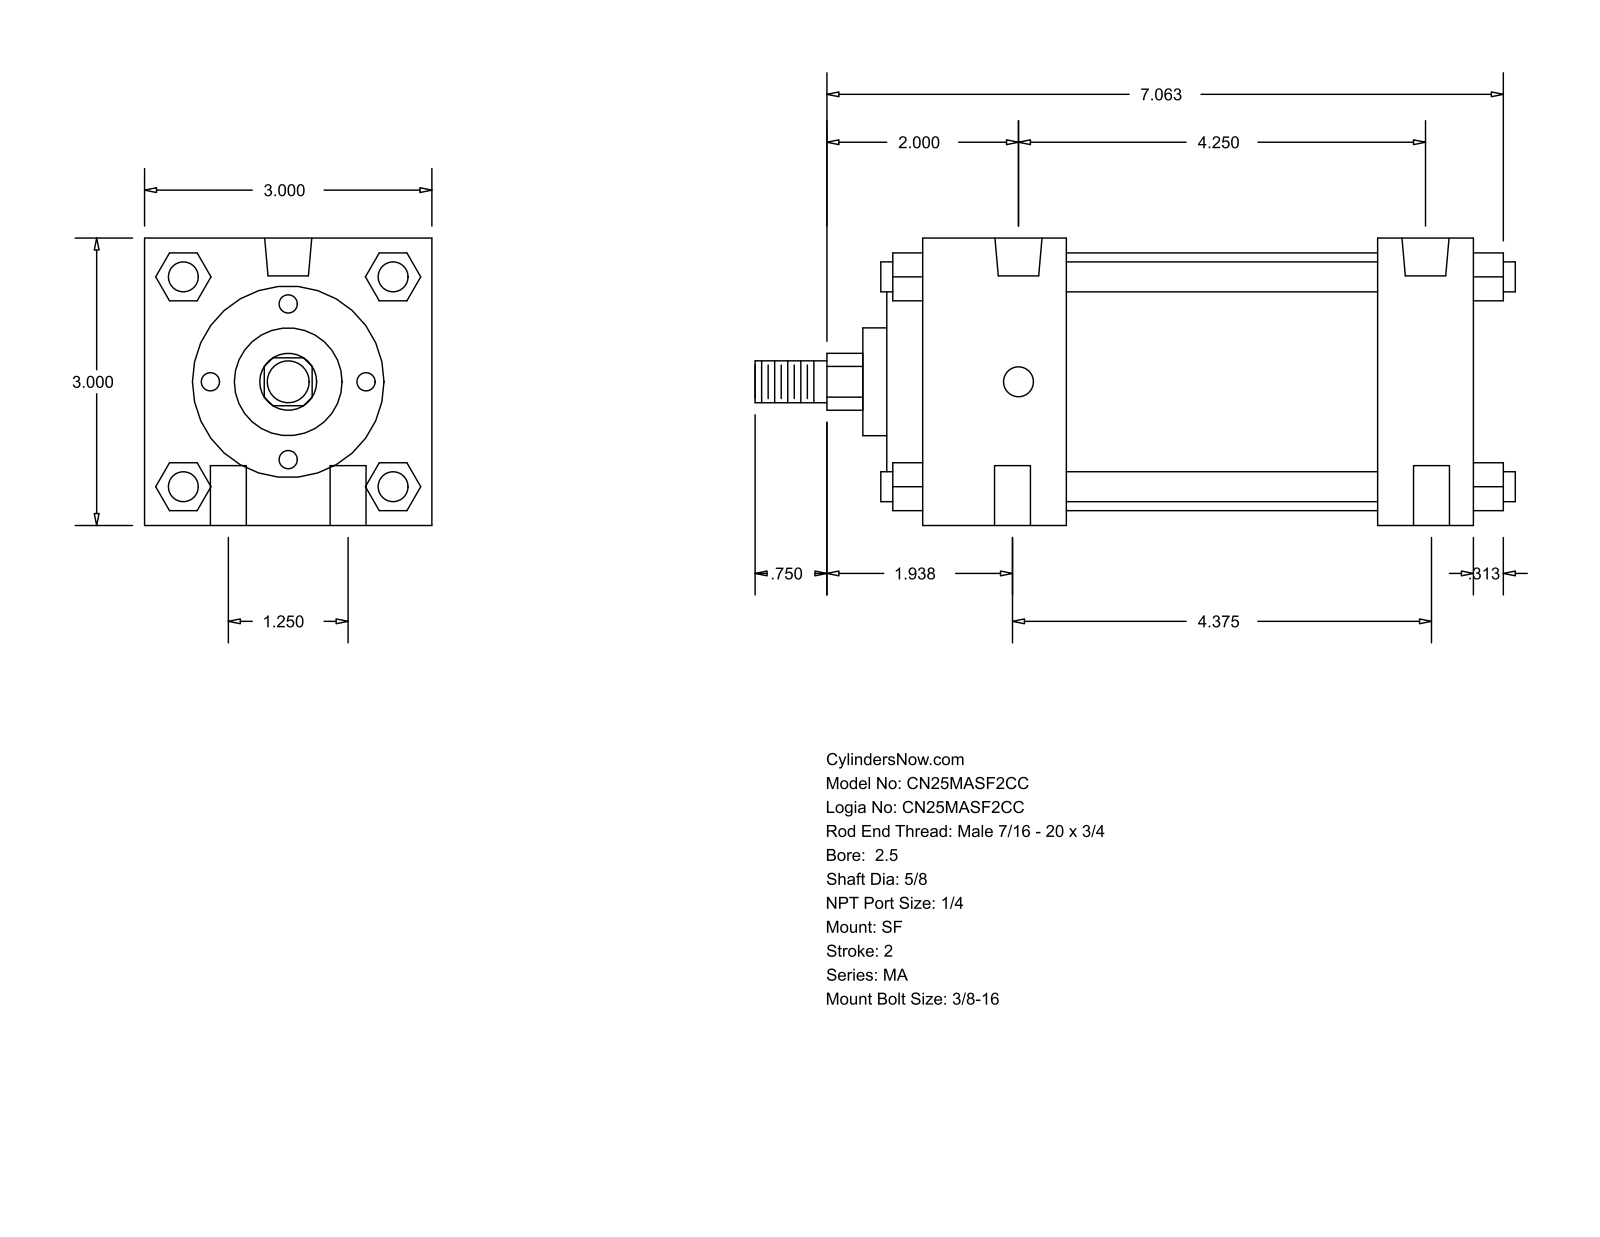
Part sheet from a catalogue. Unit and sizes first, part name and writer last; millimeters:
Units: millimetres
Overall size (bounding box): 201.61 × 76.2 × 76.2
Round holes (diameter × count): ⌀9.53 ×4, ⌀7.94 ×2, ⌀12.49 ×2
Round bosses / shafts (diameter × count): ⌀7.94 ×4, ⌀68.33 ×1, ⌀50.8 ×1, ⌀28.57 ×1, ⌀15.88 ×1, ⌀11.11 ×1
Partial cylindrical surfaces — rounded edges, fillets, slot ends (radius × count): R7.54 ×1
Main face-to-face distances: 76.2, 146.05, 25.4, 82.55, 120.65, 38.1, 107.95, 12.7, 9.52, 47.62
Hole centre spacings: 15.96, 110.69, 31.76, 107.95, 111.13, 115.58
Bodies: 0 solids, 126 faces (95 planar, 31 cylindrical, 0 other)
Part name (STEP PRODUCT): MA_SF__0250_0.625
STEP written by: GSSL Pune (CONFIG_CONTROL_DESIGN)
